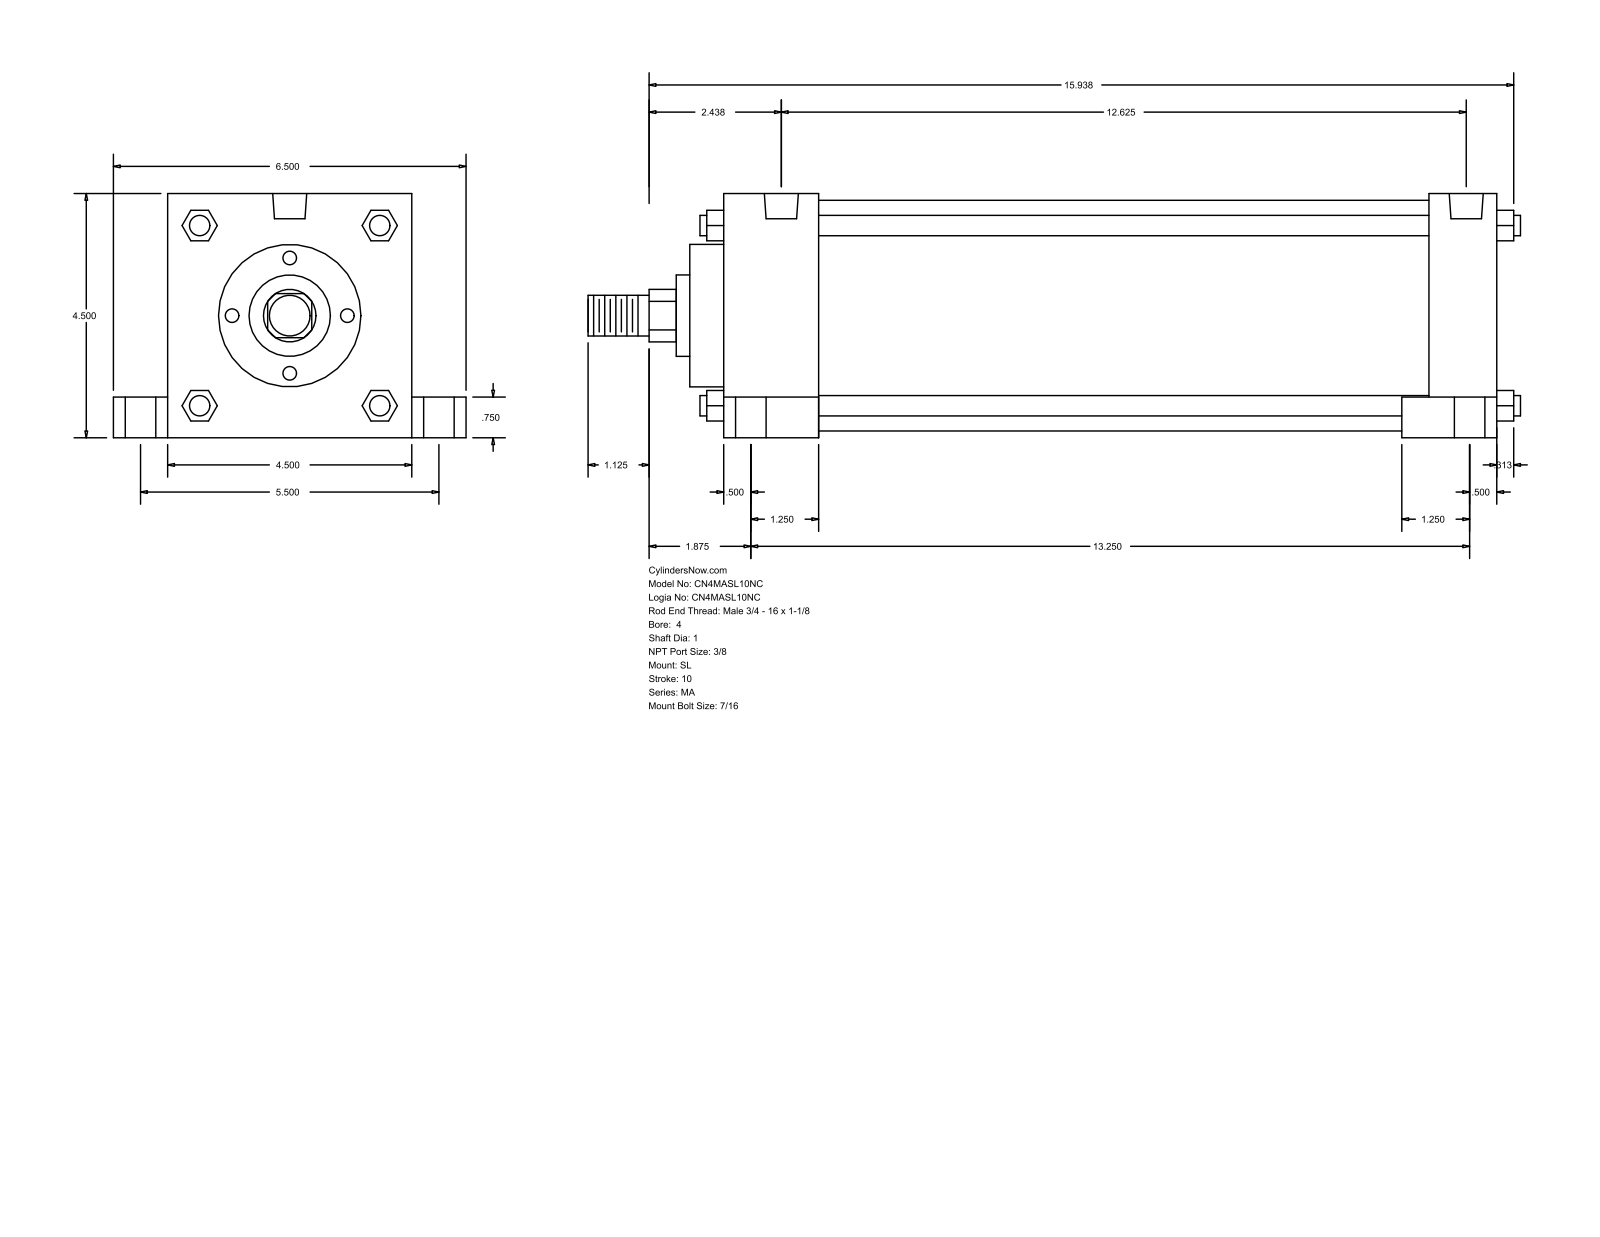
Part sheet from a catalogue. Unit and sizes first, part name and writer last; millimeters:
Units: millimetres
Overall size (bounding box): 436.56 × 165.1 × 114.3
Round holes (diameter × count): ⌀11.11 ×4, ⌀14.29 ×4, ⌀20.64 ×4, ⌀15.93 ×2
Round bosses / shafts (diameter × count): ⌀9.53 ×4, ⌀107.95 ×1, ⌀66.67 ×1, ⌀38.1 ×1, ⌀25.4 ×1, ⌀19.05 ×1
Partial cylindrical surfaces — rounded edges, fillets, slot ends (radius × count): R12.29 ×1
Main face-to-face distances: 114.3, 361.96, 44.46, 317.5, 330.2, 285.74, 31.76, 25.4, 139.7, 19.05
Hole centre spacings: 69.87, 70.14, 71.3, 72.4, 139.7, 311.15, 325.1, 329.75
Bodies: 0 solids, 150 faces (113 planar, 37 cylindrical, 0 other)
Part name (STEP PRODUCT): MA_SL__0400_1
STEP written by: GSSL Pune (CONFIG_CONTROL_DESIGN)
